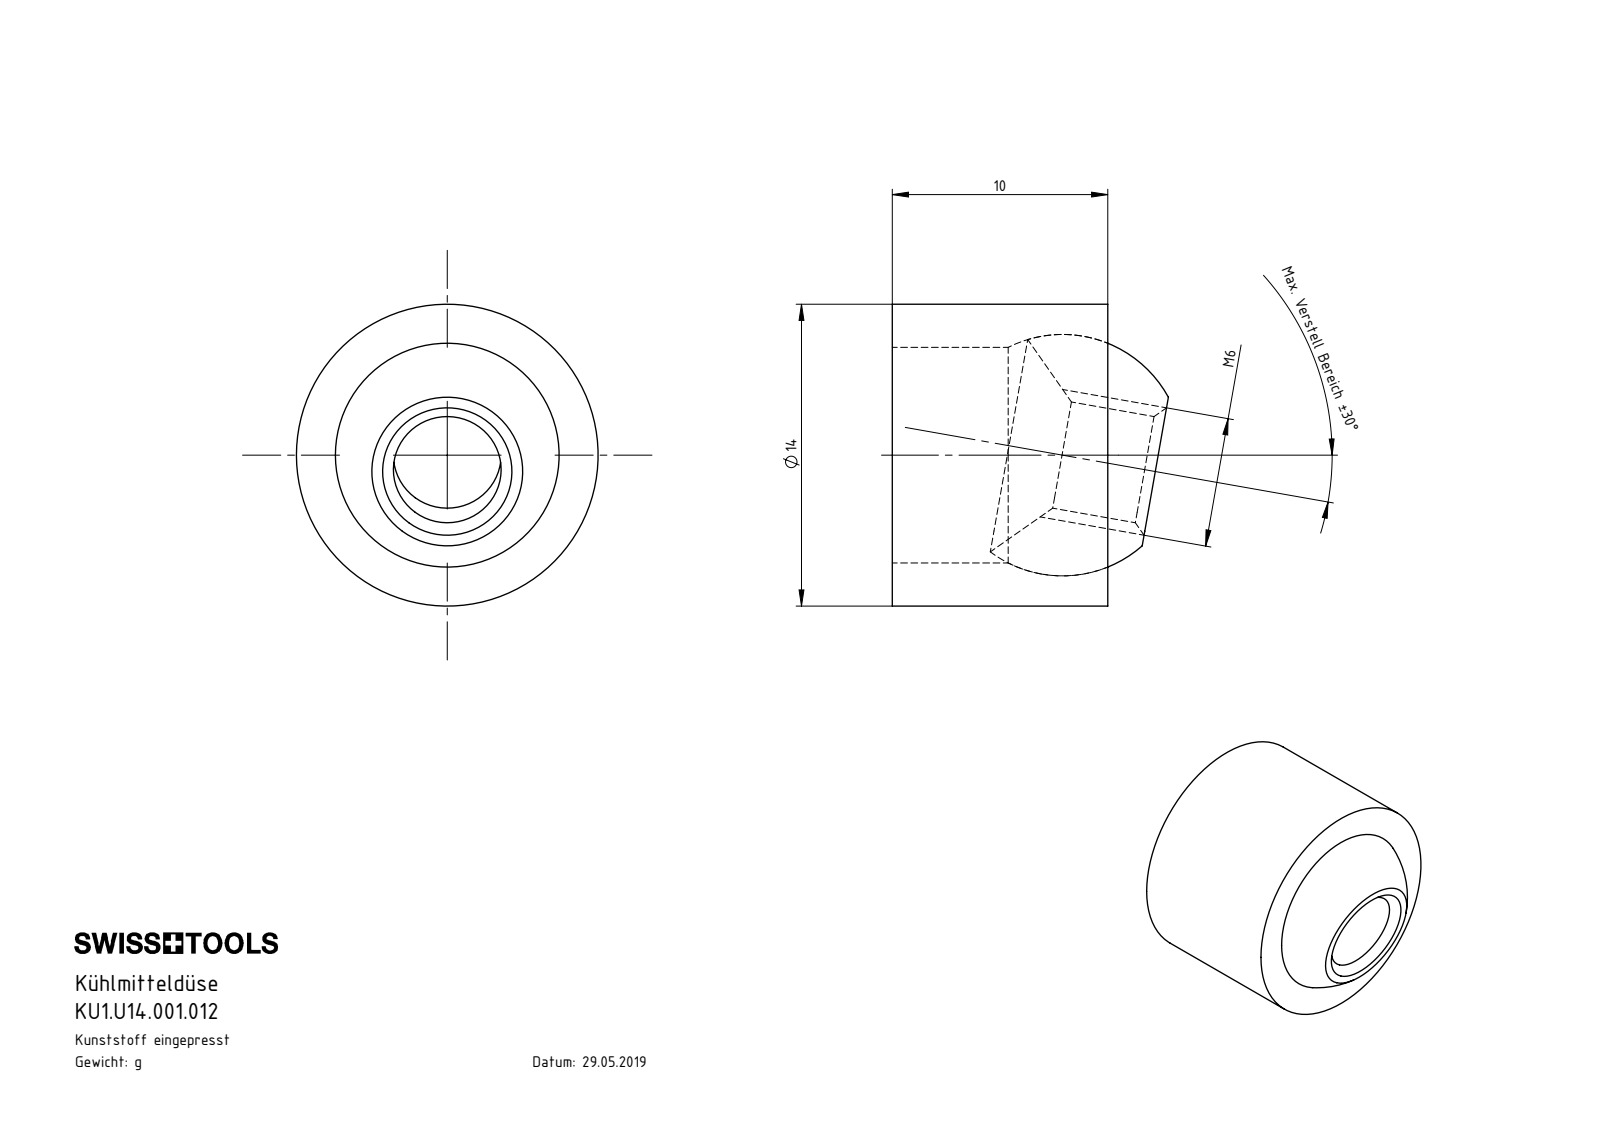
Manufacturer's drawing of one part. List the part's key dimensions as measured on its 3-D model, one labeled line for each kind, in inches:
Part name (STEP PRODUCT): KU1-U14.001.012_2; KU1-U14.001.012_1; KU1.U14.001.012
STEP written by: SolidWorks 2017 (AUTOMOTIVE_DESIGN)
Units: inches
Bodies: 2 solids, 17 faces (3 planar, 6 cylindrical, 8 other)
Overall size (bounding box): 0.551 × 0.551 × 0.504
Volume: 0.065 in³ · Surface area: 2.055 in²
Round holes (diameter × count): ⌀0.197 ×1, ⌀0.394 ×1
Round bosses / shafts (diameter × count): ⌀0.551 ×1
Main face-to-face distances: 0.394
